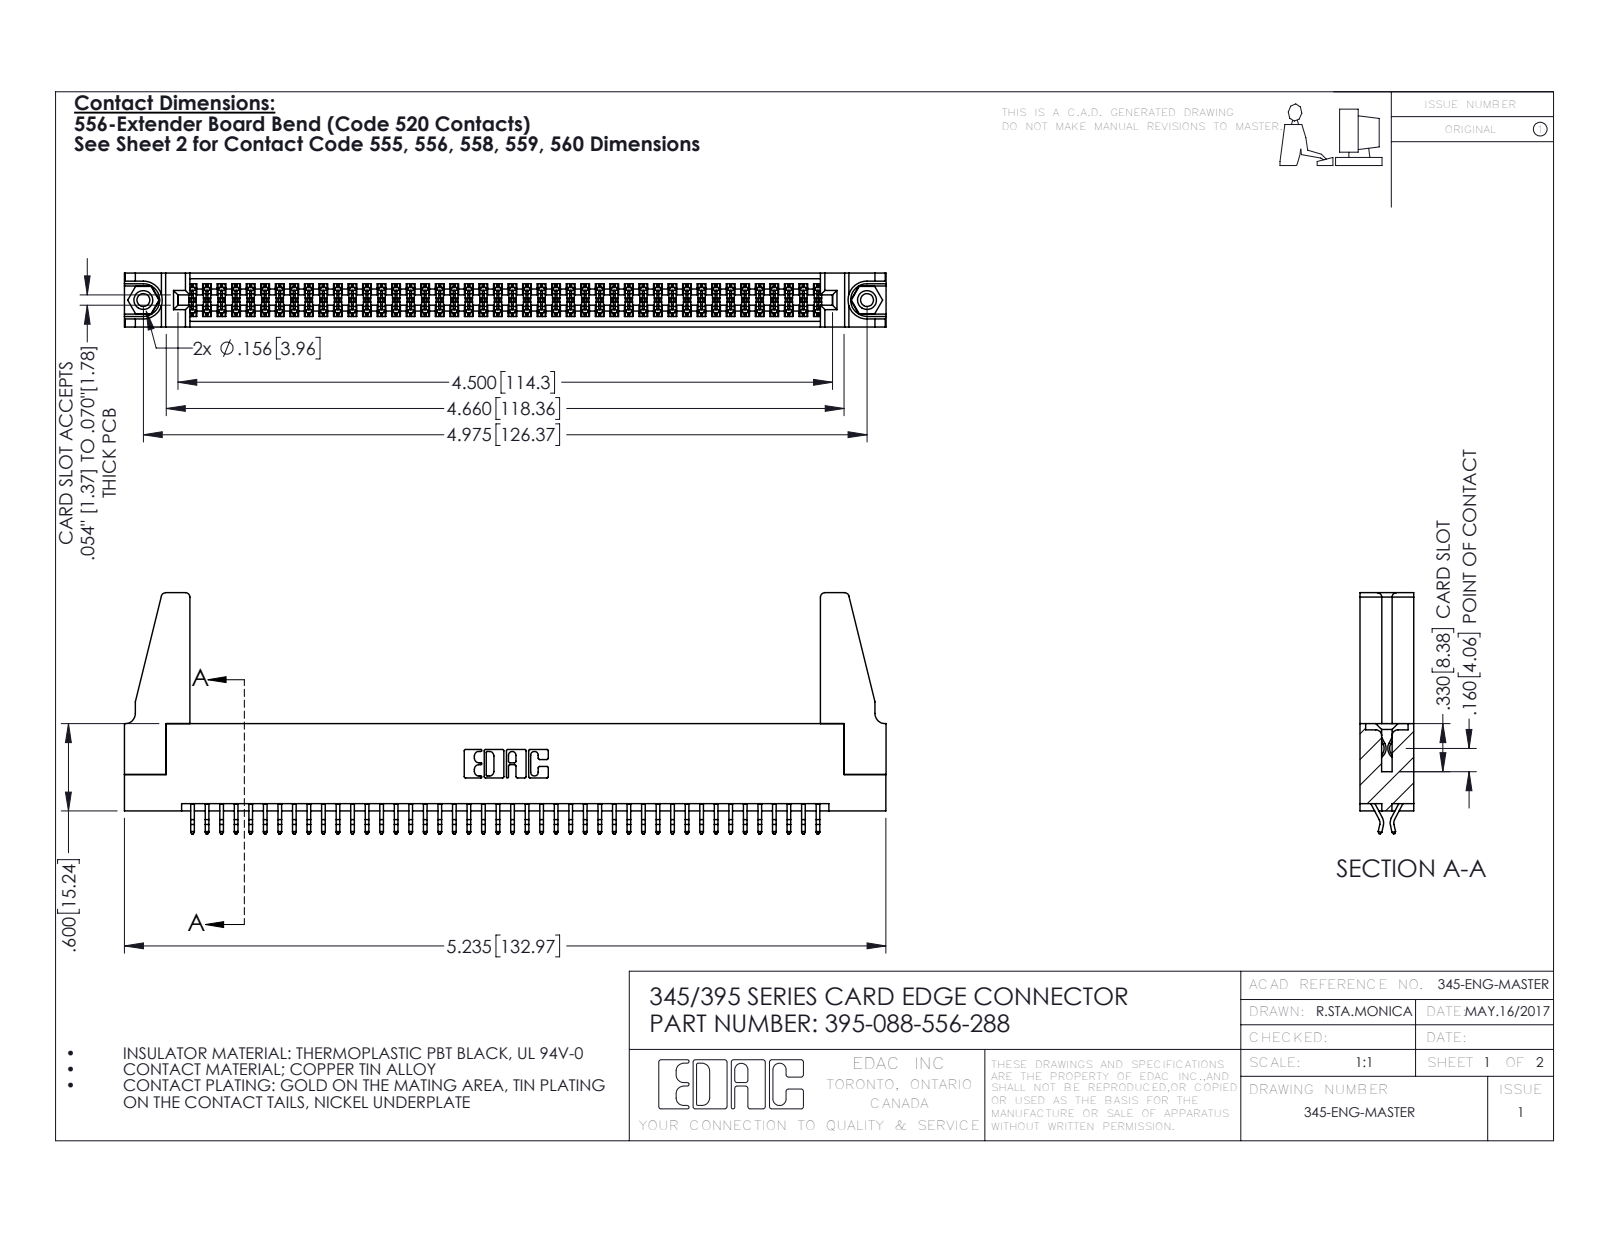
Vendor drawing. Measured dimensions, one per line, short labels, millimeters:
name: 345 Part_Flush Mounting Lugs - 0.156 Dia-TH; 345-292-001_556 Tail; 345-220-078_345-220-088; 395-088-556-288 (+1 more)
written by: SolidWorks 2016 (CONFIG_CONTROL_DESIGN)
unit: mm
bodies: 93 solids, 5178 faces (3408 planar, 1754 cylindrical, 16 other)
size: 133 × 42.1 × 9.4
volume: 16 200 mm³; area: 22 200 mm²
holes: 2× ⌀2.3, 2× ⌀3.2, 2× ⌀4, 1× ⌀1.6
bosses: 2× ⌀3.9
rounds: 132× R0.2, 22× R0.3, 8× R0.8, 6× R0.2, 6× R0.8, 3× R0.7, 2× R0.3, 2× R0.4
face distances: 1.8, 7.6, 9.4, 5.1, 0.6, 2.5, 6.9, 5.7, 4.4, 3.8
hole spacings: 6.9, 120.4, 126.4
